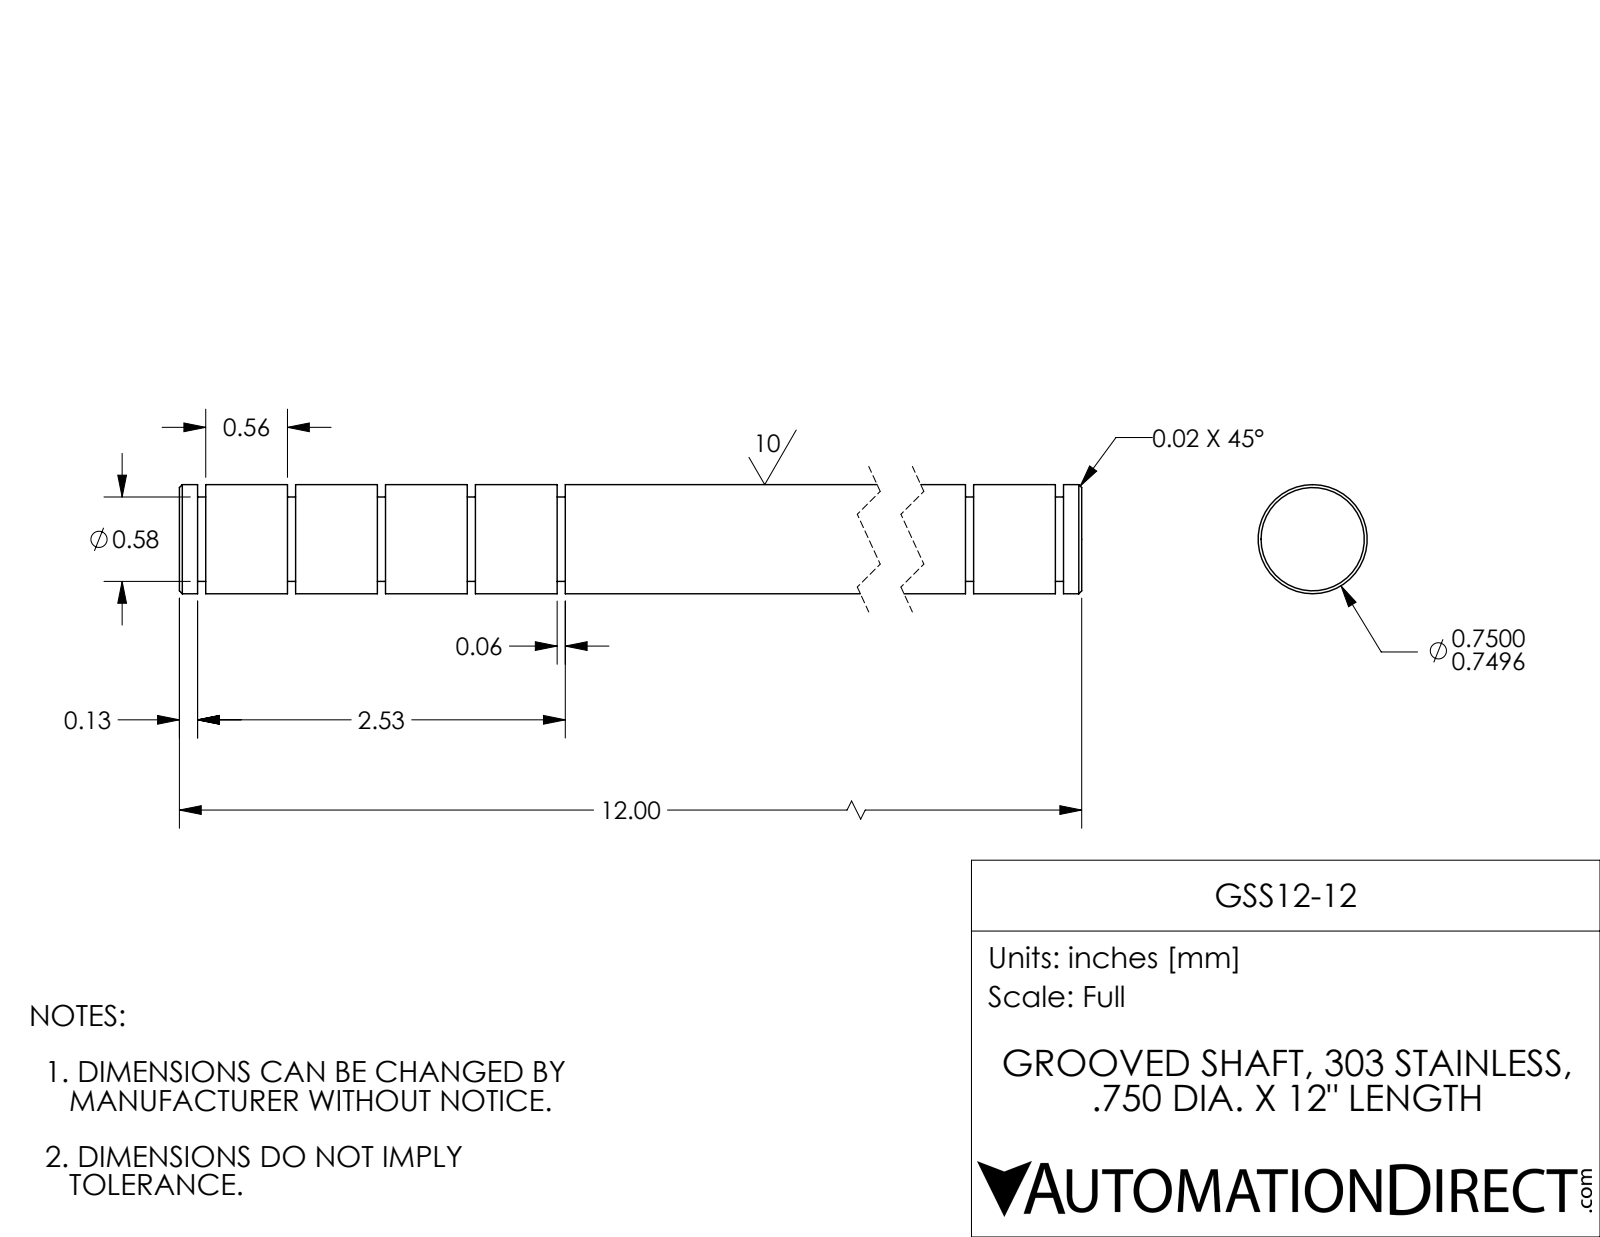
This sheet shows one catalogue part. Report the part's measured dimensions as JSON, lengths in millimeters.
{"part_name": "GSS12-12", "step_written_by": "SolidWorks 2017 (AUTOMOTIVE_DESIGN)", "units": "millimeters", "bodies": {"solids": 1, "faces": 50, "planar": 16, "cylindrical": 30, "other": 4}, "overall_size": [304.8, 19.1, 19.1], "volume_mm3": 85720, "surface_area_mm2": 20250, "round_bosses_or_shafts": [[19.1, 1], [14.7, 1]], "face_to_face_distances": [15.7, 1.4, 17.1, 31.4, 15.7, 32.8, 14.3, 281.3, 234.2, 304.8]}
